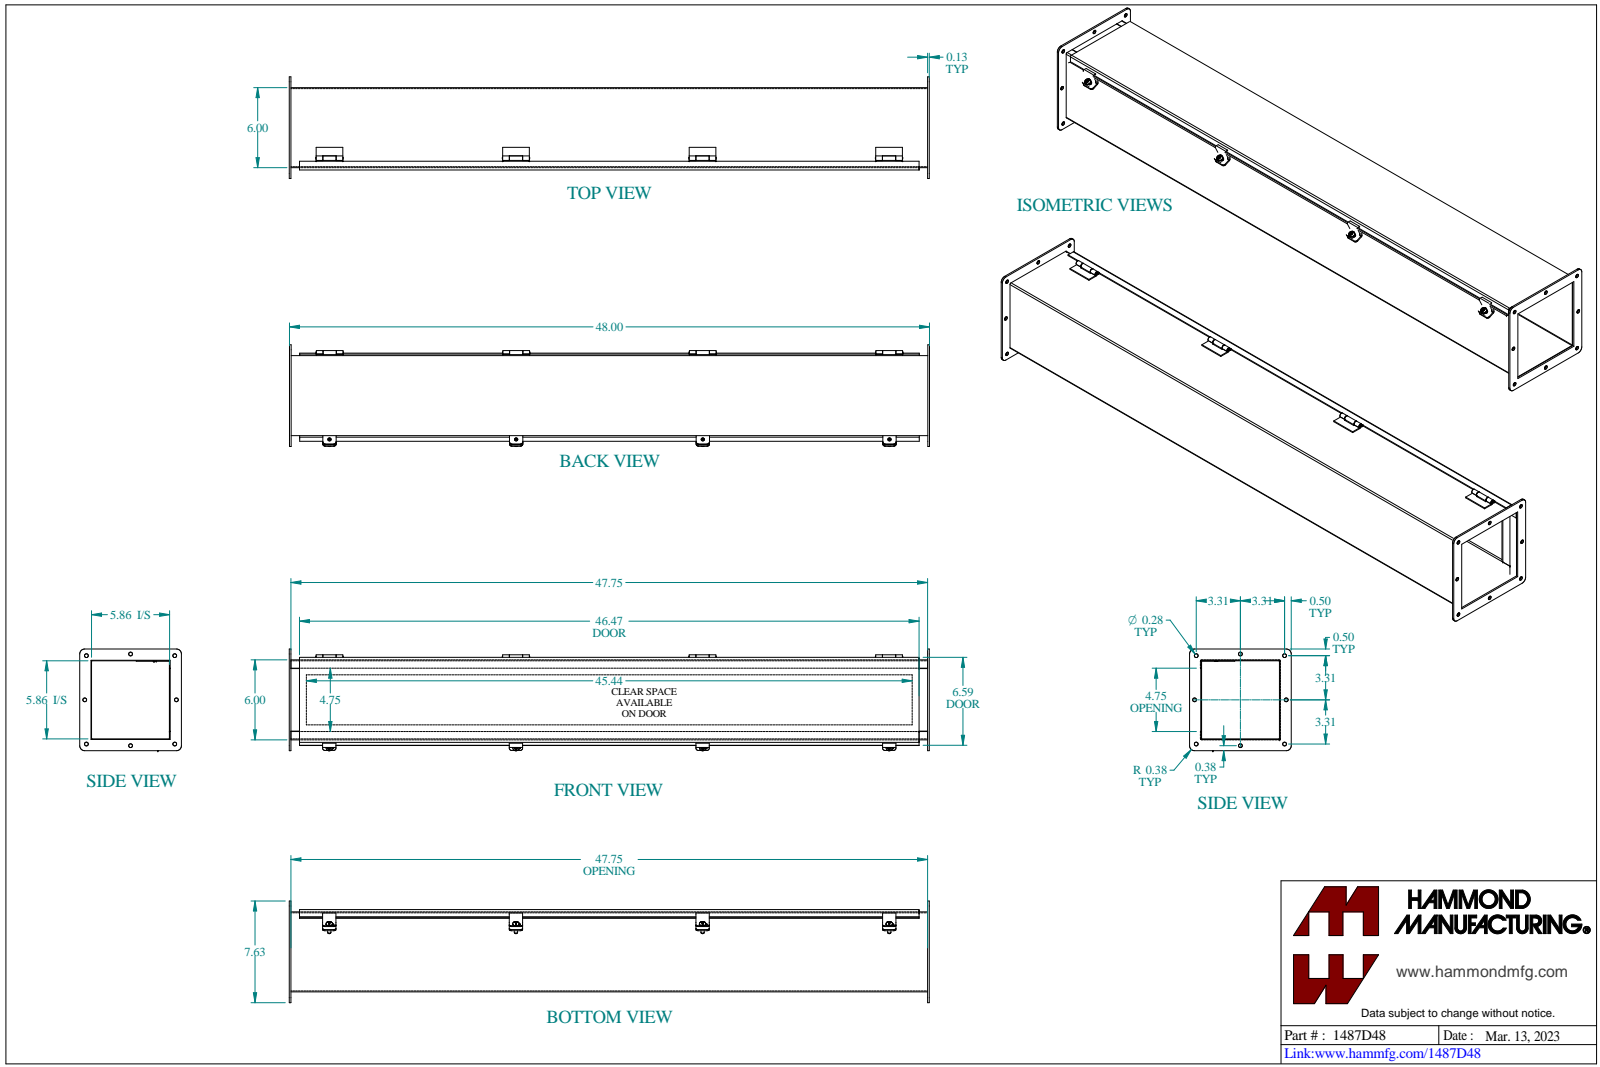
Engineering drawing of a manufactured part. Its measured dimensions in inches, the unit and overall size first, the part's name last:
Units: inches
Overall size (bounding box): 48.125 × 7.629 × 7.625
Round holes (diameter × count): ⌀0.281 ×8, ⌀0.213 ×4, ⌀0.125 ×1
Round bosses / shafts (diameter × count): ⌀0.48 ×4, ⌀0.246 ×4, ⌀0.275 ×1, ⌀0.125 ×1
Partial cylindrical surfaces — rounded edges, fillets, slot ends (radius × count): R0.188 ×16, R0.01 ×8, R0.141 ×8, R0.036 ×7, R0.108 ×7, R0.25 ×4, R0.375 ×4, R0.029 ×2
Main face-to-face distances: 0.072, 5.928, 6.1, 6, 5.856, 6.028, 6.172, 0.172, 0.1, 0.244
Hole centre spacings: 7.519, 3.315, 3.315, 6.625, 14, 4.861, 6.875, 9.369
Volume: 102.1 in³ · Surface area: 2 785 in²
Bodies: 31 solids, 698 faces (376 planar, 246 cylindrical, 76 other)
Part name (STEP PRODUCT): 1487D48
STEP written by: SolidWorks 2023 (CONFIG_CONTROL_DESIGN)
